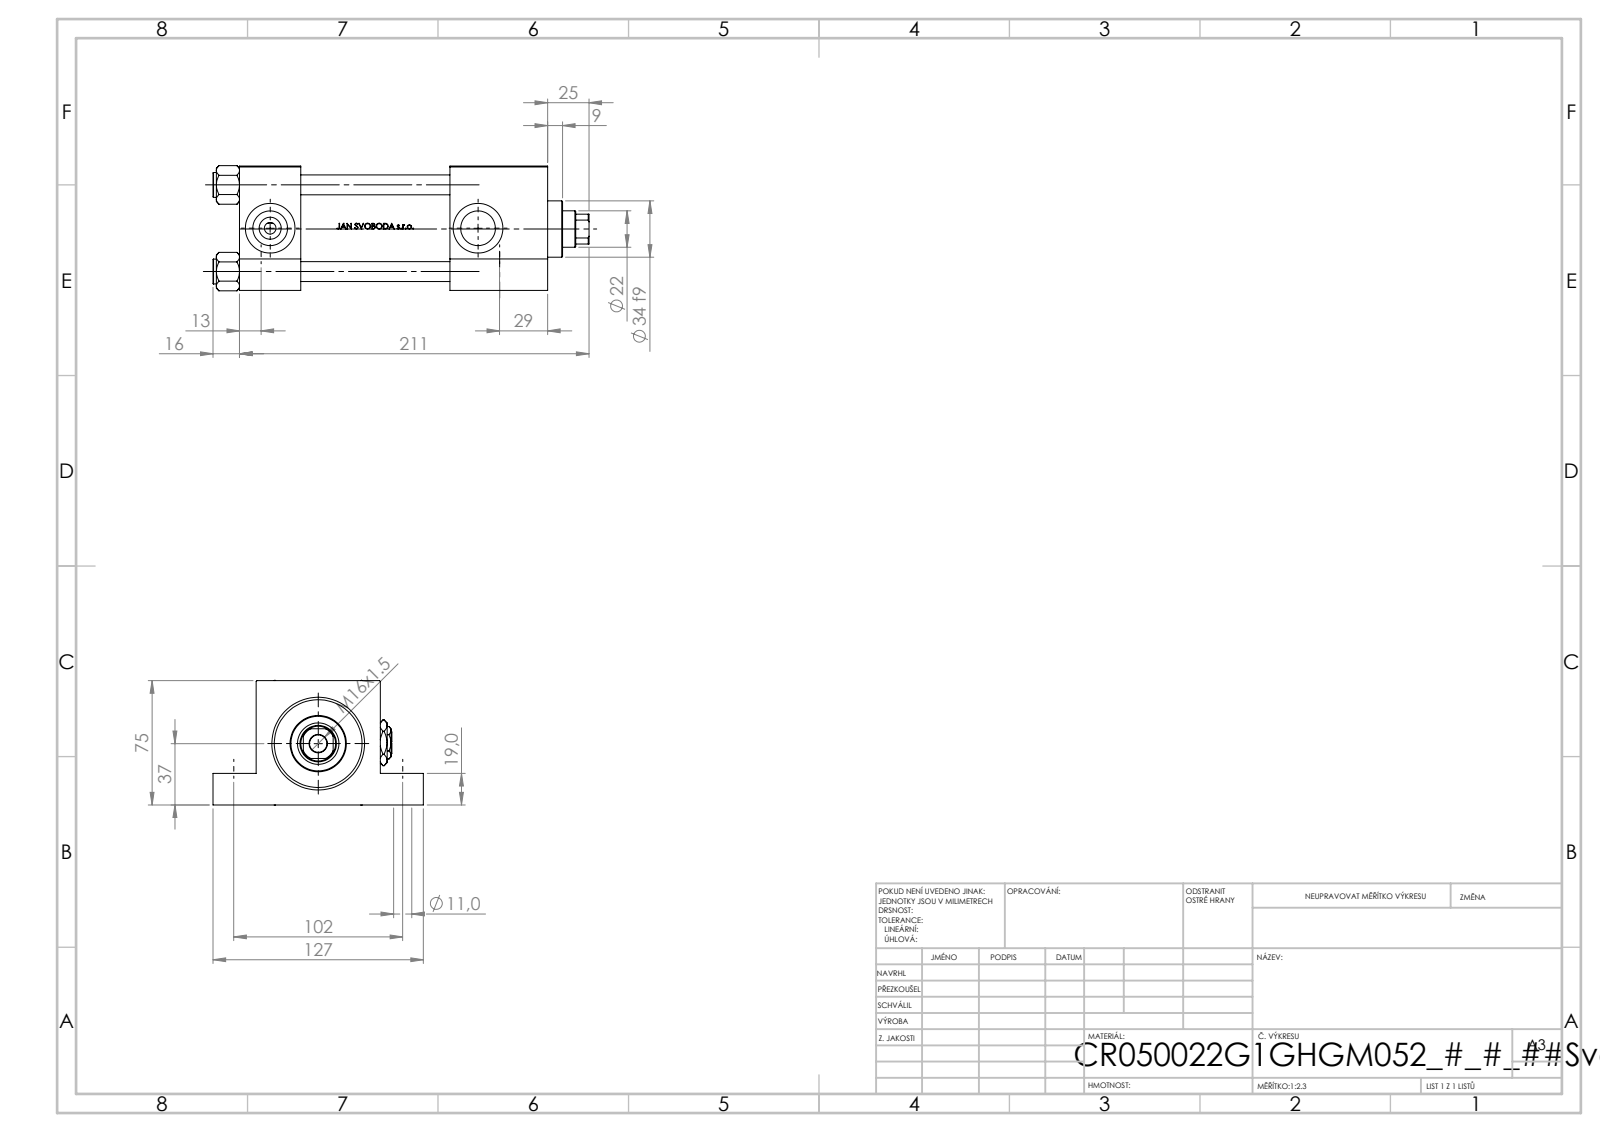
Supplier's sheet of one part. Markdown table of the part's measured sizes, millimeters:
| quantity | value |
| --- | --- |
| part name | V215CR_G_Body; NUT_M5_G; V215_VC_A; V215CR_G_TYCINKA (+2 more) |
| STEP written by | SolidWorks 2019 (CONFIG_CONTROL_DESIGN) |
| units | millimeters |
| bodies | 12 solids, 1134 faces (454 planar, 128 cylindrical, 552 other) |
| overall size | 227 × 127 × 75.54 |
| volume | 795 028 mm³ |
| surface area | 178 997 mm² |
| round holes (diameter × count) | 11 × 4, 12 × 4, 7 × 2, 20.96 × 2, 30 × 2, 10.5 × 1, 22 × 1, 25 × 1, 41 × 1, 50 × 1, 53 × 1 |
| round bosses / shafts (diameter × count) | 15 × 4, 56 × 1, 34 × 1 |
| partial cylindrical surfaces (radius × count) | 10.5 × 1 |
| main face-to-face distances | 75, 37, 127, 186, 149, 19, 56, 90, 59, 26 |
| hole center spacings | 52.3, 36.63, 37.34, 73.96, 102, 144, 176.47, 125.5 |
